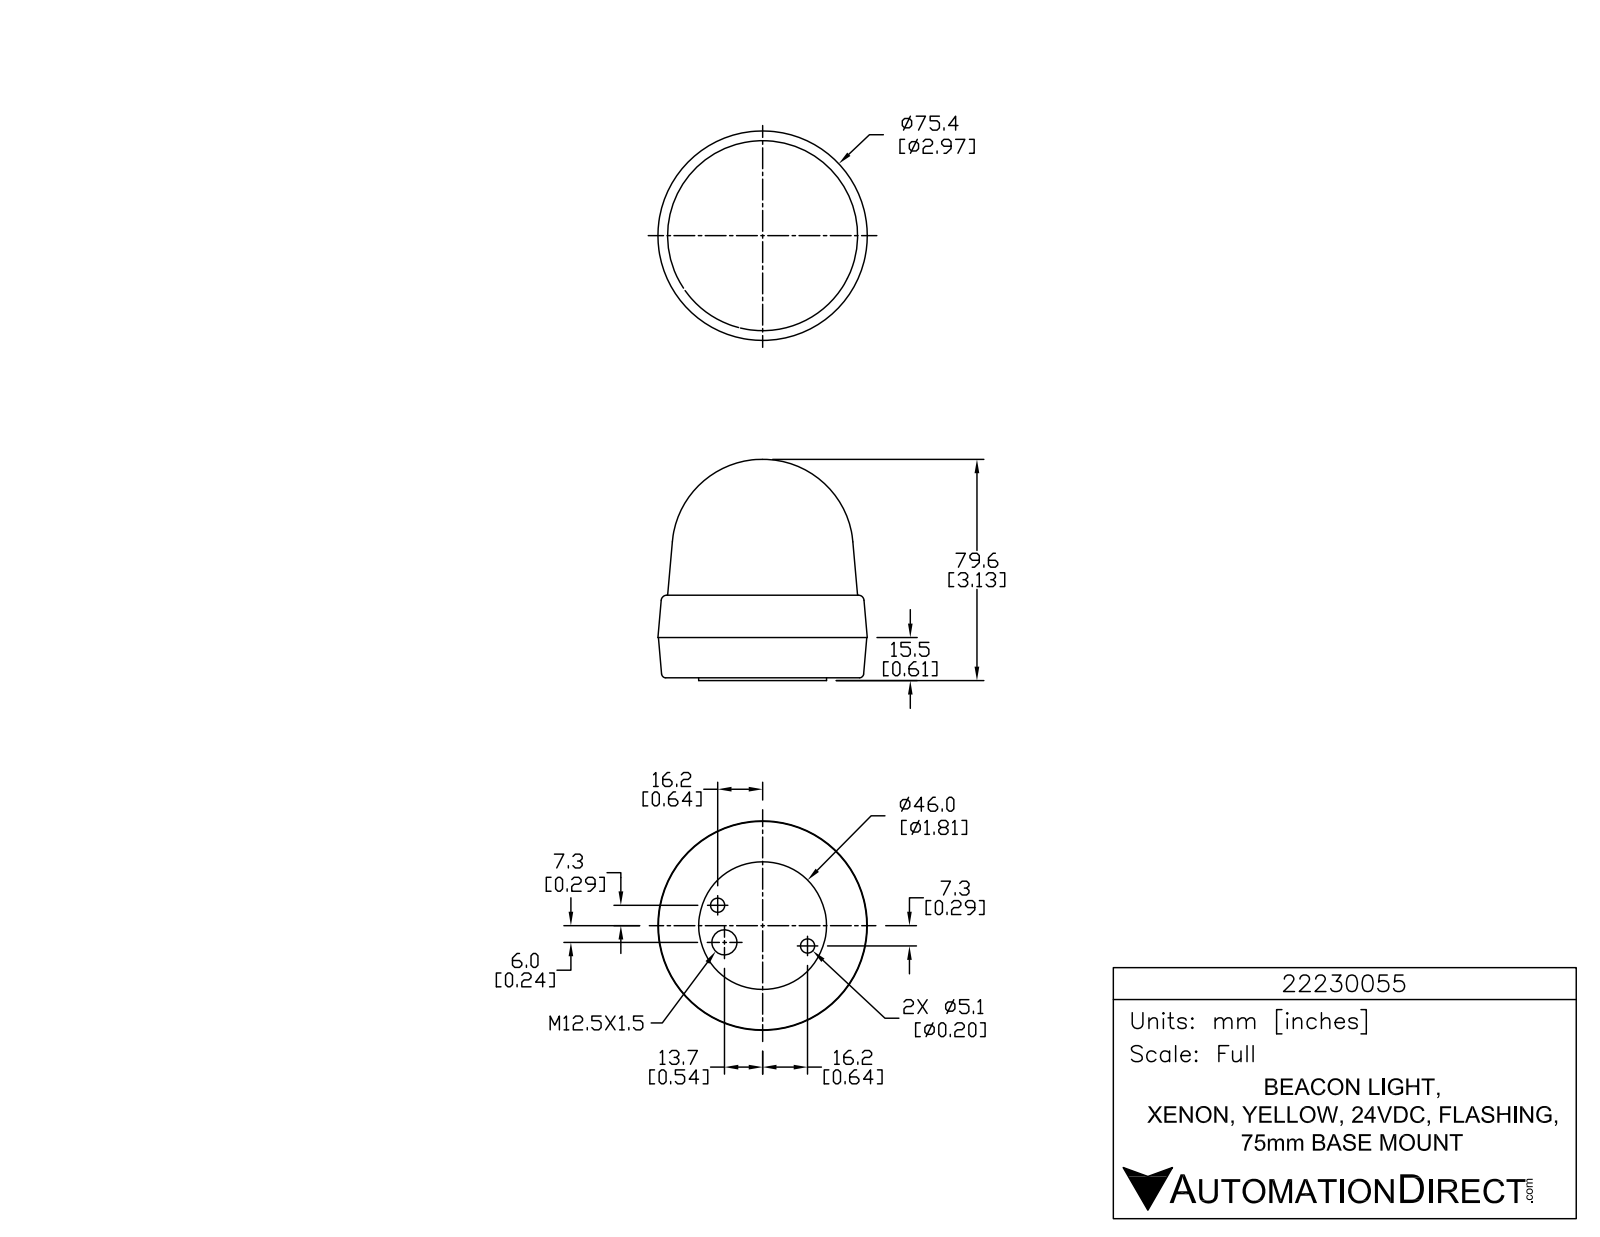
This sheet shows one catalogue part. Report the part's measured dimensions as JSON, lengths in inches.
{"part_name": "22230055", "step_written_by": "SolidWorks 2015 (AUTOMOTIVE_DESIGN)", "units": "inches", "bodies": {"solids": 1, "faces": 773, "planar": 526, "cylindrical": 163, "other": 84}, "overall_size": [3.133, 2.967, 2.967], "volume_in3": 15.79, "surface_area_in2": 33.7, "round_holes": [[0.059, 3], [0.201, 2], [0.354, 1]], "round_bosses_or_shafts": [[0.339, 3], [0.084, 3], [1.811, 1]], "partial_cylinders_radius": [[0.005, 9], [0.005, 6], [0.012, 6], [0.012, 6], [0.012, 6], [0.196, 6], [0.005, 3], [0.005, 3]], "face_to_face_distances": [0.039, 1.209, 1.17, 0.61, 0.571, 0.599, 1.566, 1.527, 0.956, 0.357], "hole_center_spacings": [0.534, 1.179, 1.398]}
